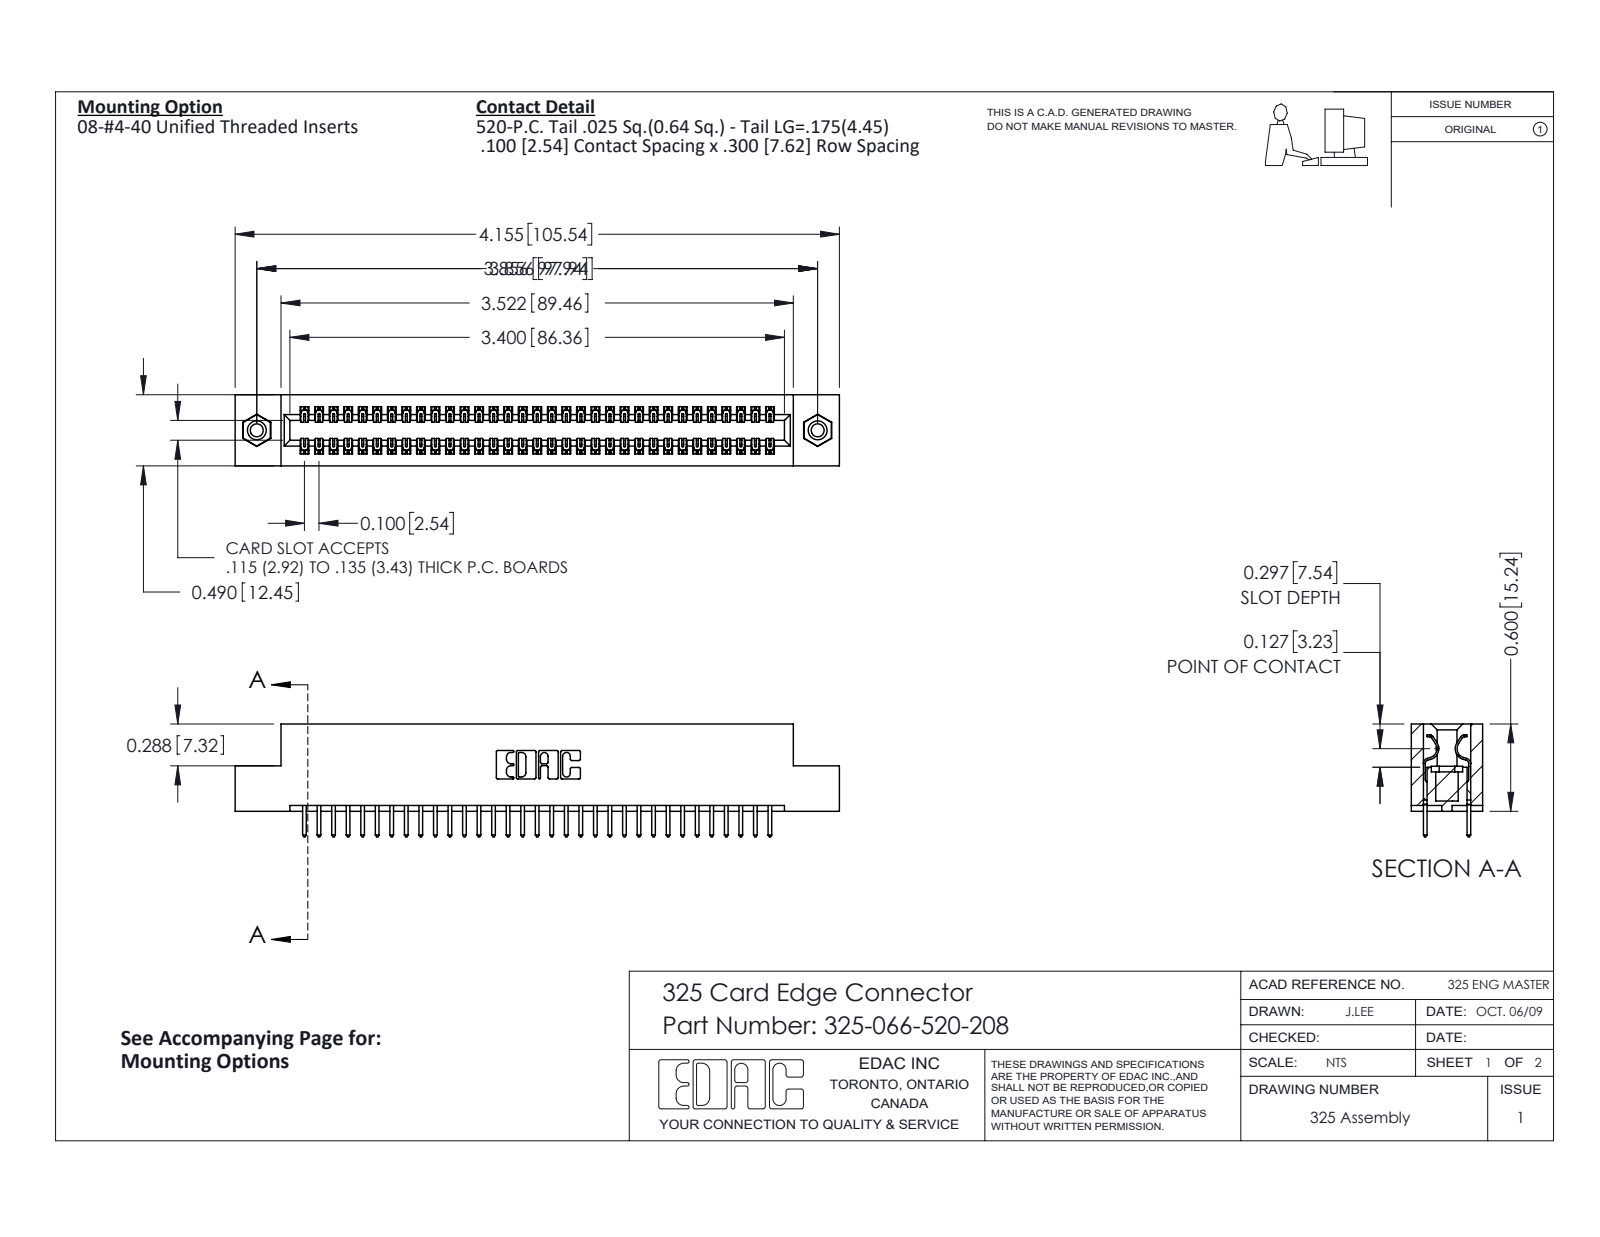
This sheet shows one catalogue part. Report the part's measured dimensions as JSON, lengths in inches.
{"part_name": "345-250-001_345-250-003-102; 325-292-001_325-293-120; 325 Part_TI; 325-066-520-208", "step_written_by": "SolidWorks 2016 (CONFIG_CONTROL_DESIGN)", "units": "inches", "bodies": {"solids": 69, "faces": 3606, "planar": 2478, "cylindrical": 1112, "other": 16}, "overall_size": [4.155, 0.775, 0.49], "volume_in3": 0.825, "surface_area_in2": 24.86, "round_holes": [[0.089, 2], [0.125, 2], [0.16, 2]], "round_bosses_or_shafts": [[0.155, 2]], "partial_cylinders_radius": [[0.006, 99], [0.01, 66], [0.01, 22], [0.007, 6], [0.031, 6], [0.026, 3], [0.014, 2], [0.022, 2]], "face_to_face_distances": [0.083, 0.407, 0.49, 0.3, 0.107, 0.383, 0.025, 0.325, 0.275, 0.56], "hole_center_spacings": [3.856]}
